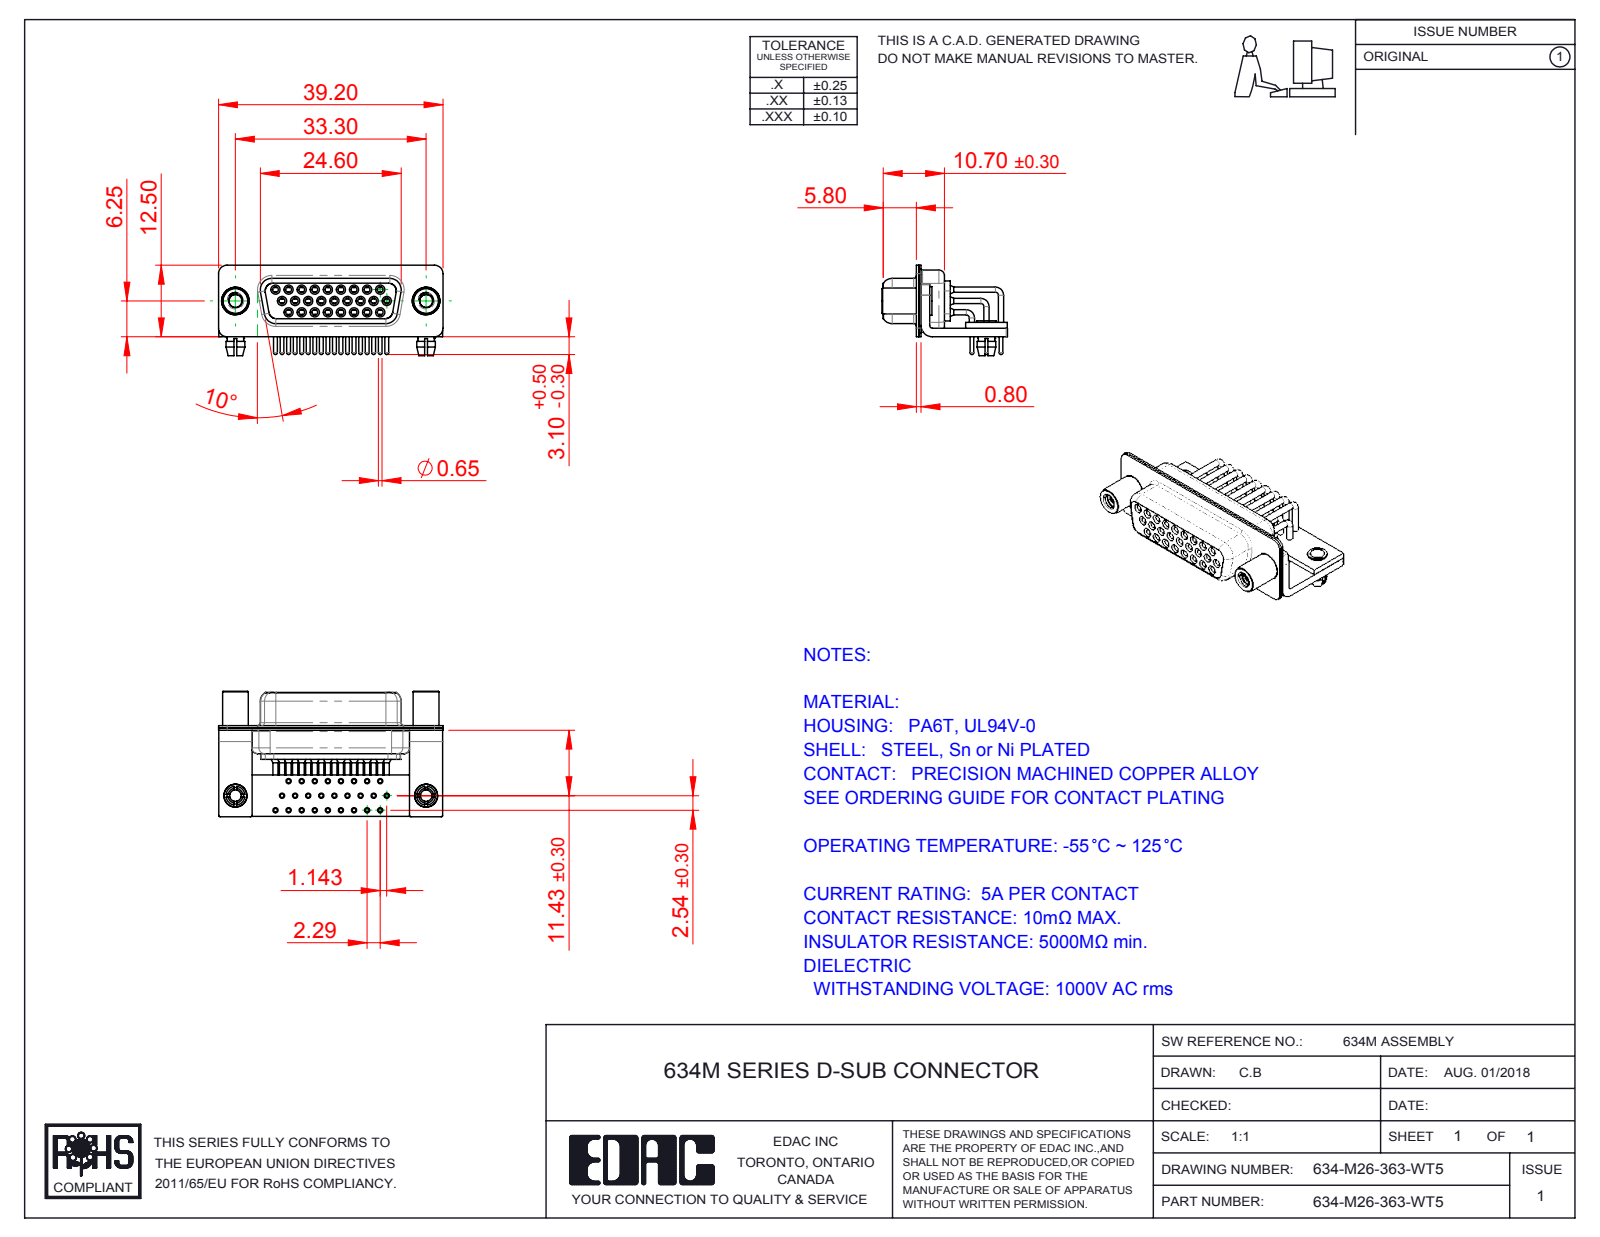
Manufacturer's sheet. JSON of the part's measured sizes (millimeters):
{"part_name": "634M Housing_26 Contacts; 634-M26-363-WT5; 634M Board Lock; 634M Stabilizer Board_26 Contacts (+7 more)", "step_written_by": "SolidWorks 2016 (CONFIG_CONTROL_DESIGN)", "units": "millimeters", "bodies": {"solids": 36, "faces": 1901, "planar": 533, "cylindrical": 883, "other": 485}, "overall_size": [39.2, 21.9, 15.8], "volume_mm3": 3236, "surface_area_mm2": 10333, "round_holes": [[2, 28], [0.9, 26], [1, 26], [1.1, 26], [1.7, 26], [1.8, 26], [2.26, 2], [2.5, 2], [3.2, 2], [4, 2], [4.8, 2]], "round_bosses_or_shafts": [[0.9, 27], [1.6, 26], [1.5, 26], [0.65, 26], [5, 2], [4.9, 2], [4.5, 2], [4, 2]], "partial_cylinders_radius": [[0.25, 16], [1.5, 16], [2, 13], [1.35, 8], [1.6, 8], [0.5, 5], [0.6, 4], [0.65, 4]], "face_to_face_distances": [0.4, 2.3, 1.9, 0.8, 1.5, 1, 9.35, 8.5, 1.45, 8.95], "hole_center_spacings": [4.57, 2.29, 2.28, 3.96, 6.05, 6.86, 4.27, 2.78]}
